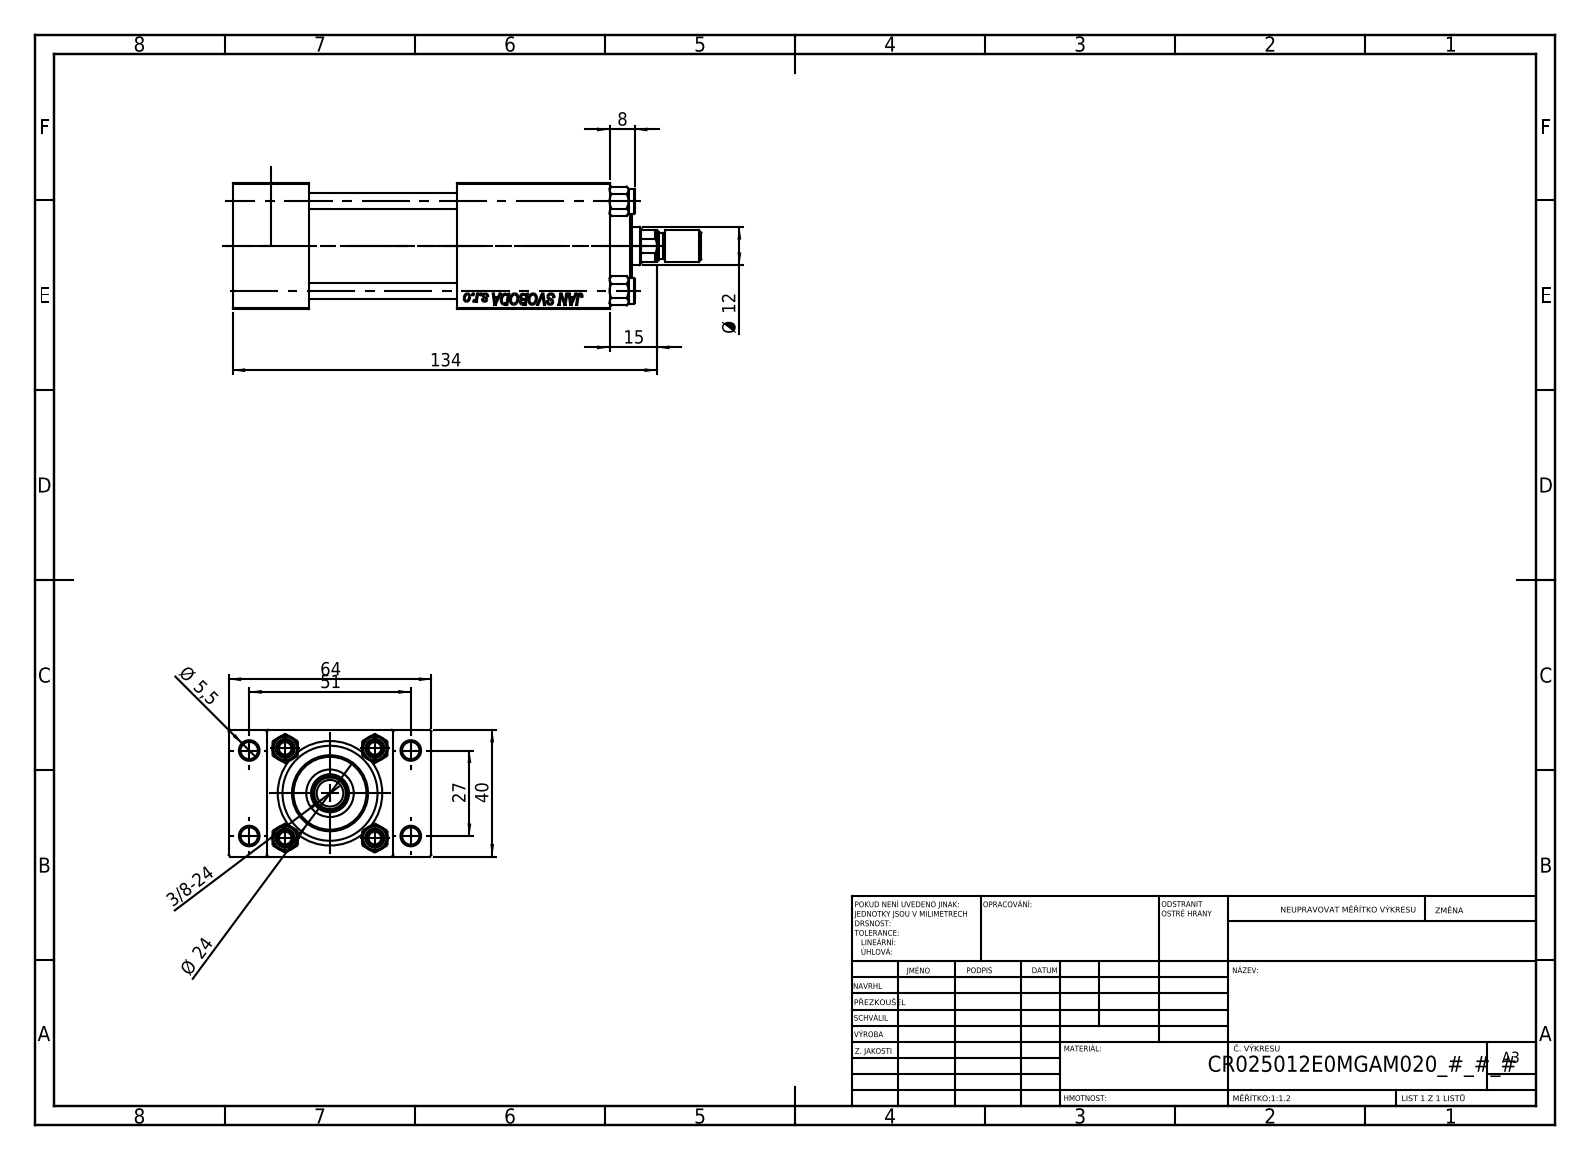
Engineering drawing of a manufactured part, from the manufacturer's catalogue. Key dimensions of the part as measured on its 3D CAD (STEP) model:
Part name (STEP PRODUCT): V215_VC_A; V215CR_TYCINKA_E; V215CR_E_Body; ROD_END_AH (+2 more)
STEP written by: SolidWorks 2019 (CONFIG_CONTROL_DESIGN)
Units: millimetres
Bodies: 12 solids, 1150 faces (501 planar, 91 cylindrical, 558 other)
Overall size (bounding box): 148 × 64 × 40
Volume: 164 946 mm³ · Surface area: 62 715 mm²
Round holes (diameter × count): ⌀5 ×4, ⌀5.5 ×4, ⌀20 ×3, ⌀7 ×2, ⌀13.16 ×2, ⌀6.5 ×1, ⌀12 ×1, ⌀15 ×1, ⌀25 ×1, ⌀30 ×1
Round bosses / shafts (diameter × count): ⌀8 ×5, ⌀31 ×1, ⌀24 ×1, ⌀10 ×1
Partial cylindrical surfaces — rounded edges, fillets, slot ends (radius × count): R5.5 ×1
Main face-to-face distances: 40, 24, 12, 52, 119, 95, 90.3, 66.3, 28.7, 64
Hole centre spacings: 11.37, 20.01, 28.3, 28.85, 29.89, 39.66, 48.34, 27
